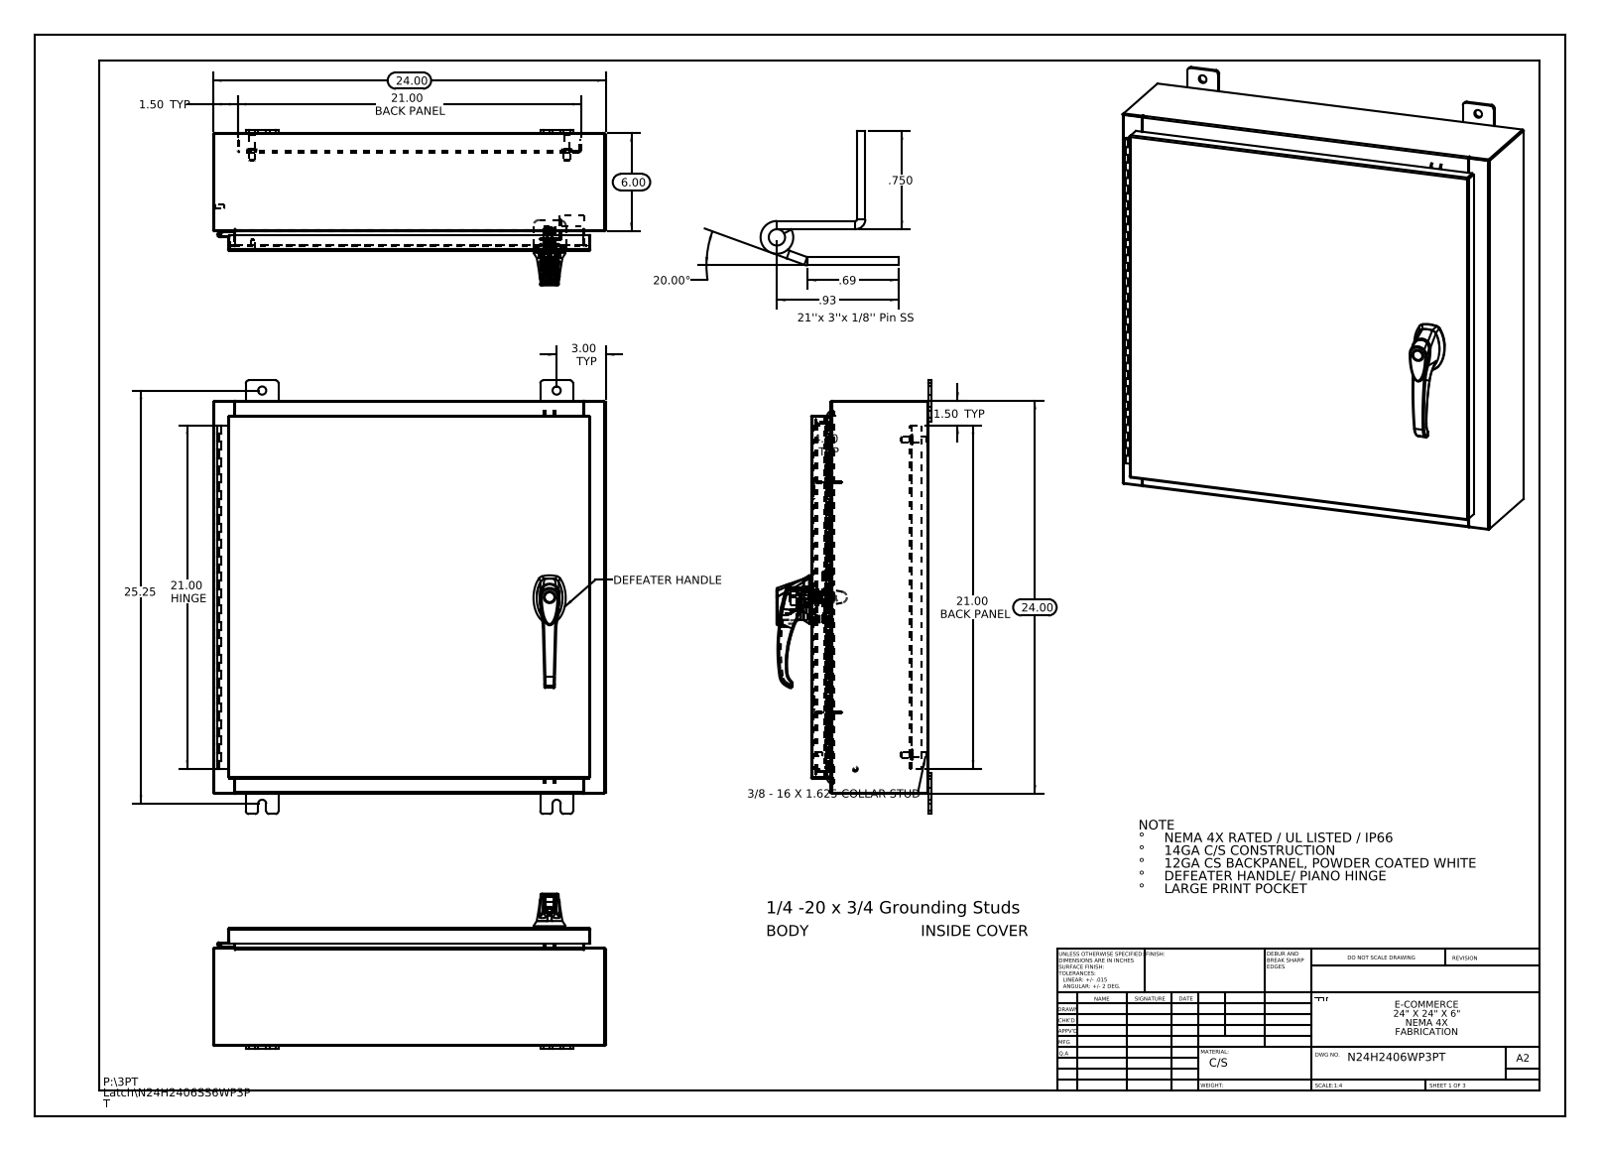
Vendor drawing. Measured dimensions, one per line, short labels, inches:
name: g26103103_26163303; N24H2406SS6WP3PT Hinge Enclosure Side2; 022151; 2616310101 (+8 more)
written by: SolidWorks 2013 (CONFIG_CONTROL_DESIGN)
unit: in
bodies: 31 solids, 2412 faces (865 planar, 893 cylindrical, 654 other)
size: 26.5 × 24 × 9.495
volume: 209.1 in³; area: 5 137 in²
holes: 8× ⌀0.5, 4× ⌀0.25, 3× ⌀0.138, 3× ⌀0.161, 2× ⌀0.079, 2× ⌀0.203, 2× ⌀0.313, 2× ⌀0.437, 1× ⌀0.125, 1× ⌀0.125, 1× ⌀0.197, 1× ⌀0.276
bosses: 4× ⌀0.625, 4× ⌀0.375, 4× ⌀0.33, 1× ⌀1.181, 1× ⌀0.748, 1× ⌀0.68, 1× ⌀0.661, 1× ⌀0.639
rounds: 37× R0.118, 33× R0.006, 24× R0.19, 22× R0.013, 18× R0.088, 15× R0.039, 12× R0.028, 6× R0.008
face distances: 0.075, 7.126, 23.925, 7.051, 7.201, 0.104, 1, 1.075, 6.051, 6.126
hole spacings: 7.68, 0.295, 0.625, 0.841, 1.25, 1.313, 1.561, 1.858
